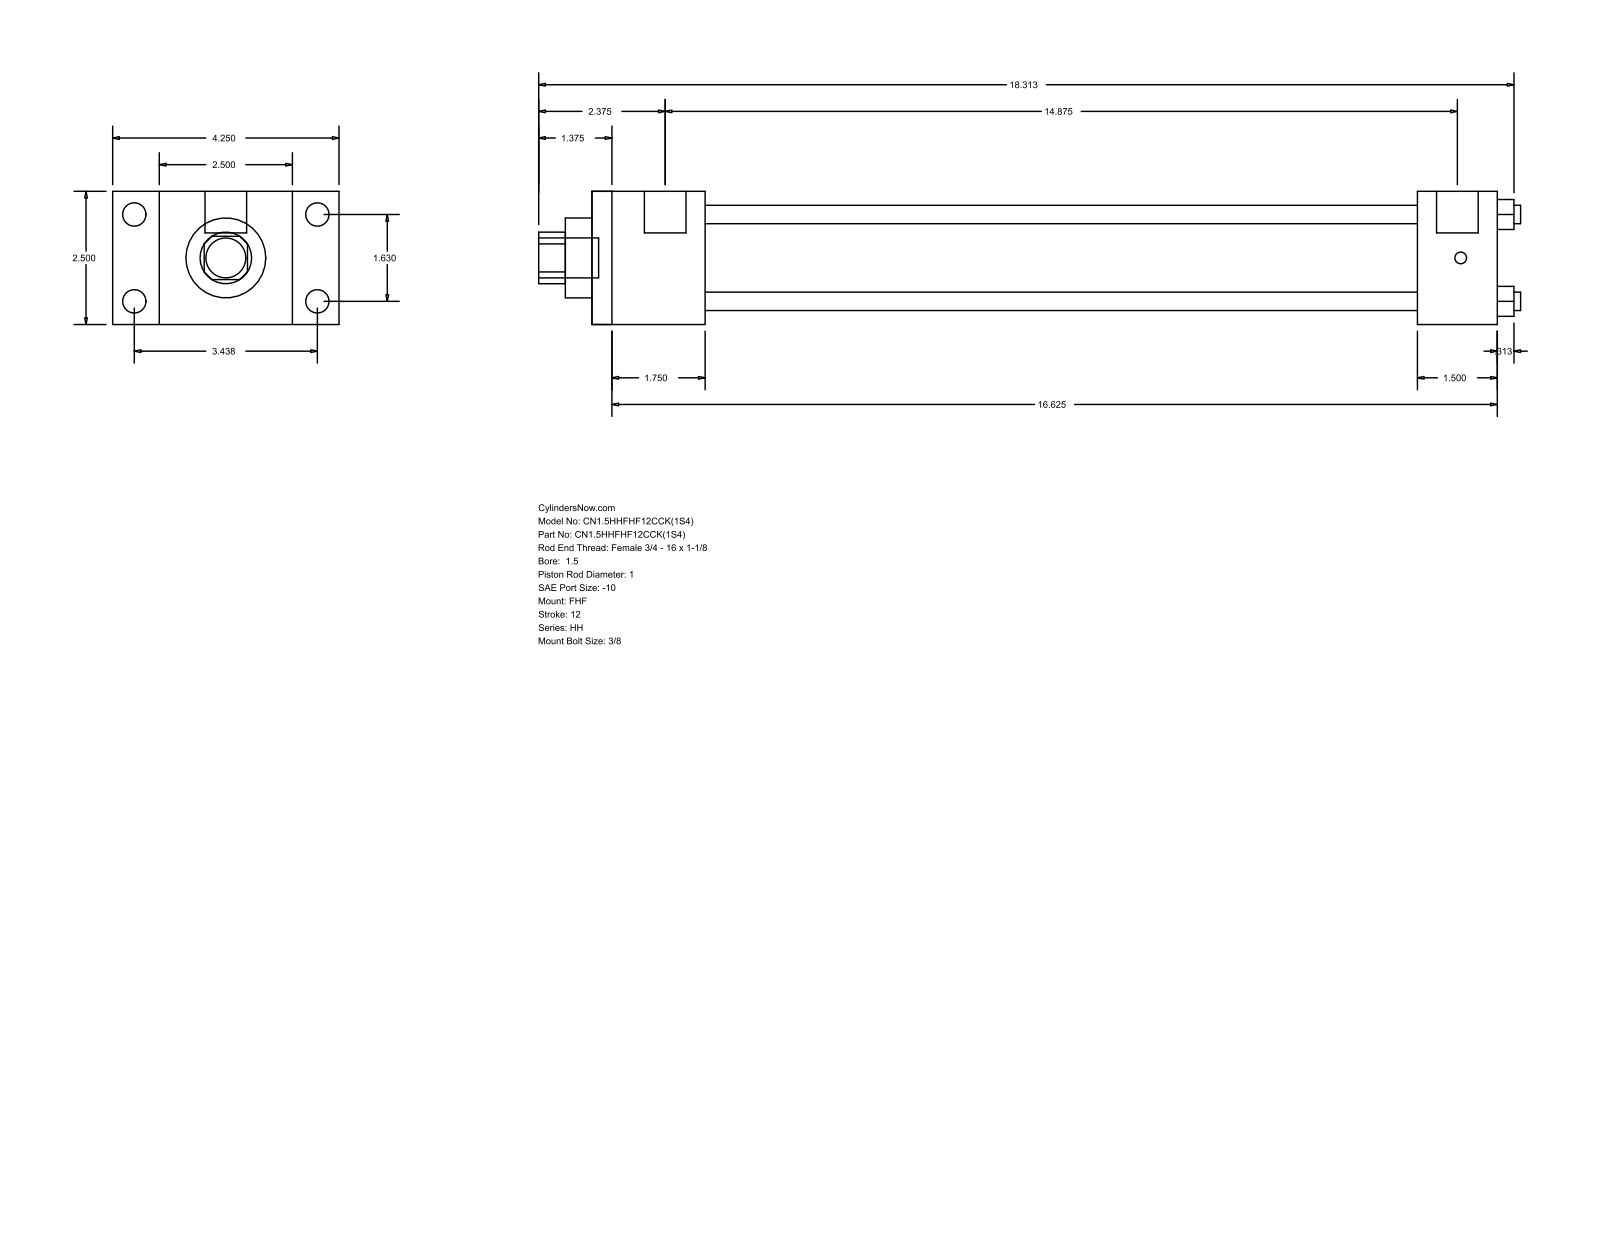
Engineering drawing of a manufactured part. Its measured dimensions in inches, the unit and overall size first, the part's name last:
Units: inches
Overall size (bounding box): 18.437 × 4.25 × 2.5
Round holes (diameter × count): ⌀0.345 ×4, ⌀1 ×1, ⌀1.5 ×1, ⌀1.75 ×1
Round bosses / shafts (diameter × count): ⌀0.438 ×4, ⌀0.219 ×4, ⌀0.781 ×2, ⌀0.75 ×1
Partial cylindrical surfaces — rounded edges, fillets, slot ends (radius × count): R0.484 ×1
Main face-to-face distances: 2.5, 0.875, 3.375, 2.125, 4.25, 17, 14.875, 15.5, 13.375, 1.5
Hole centre spacings: 1.152, 1.63, 2.305
Bodies: 0 solids, 88 faces (60 planar, 28 cylindrical, 0 other)
Part name (STEP PRODUCT): HH_FHF__0150_1
STEP written by: GSSL Pune (CONFIG_CONTROL_DESIGN)
